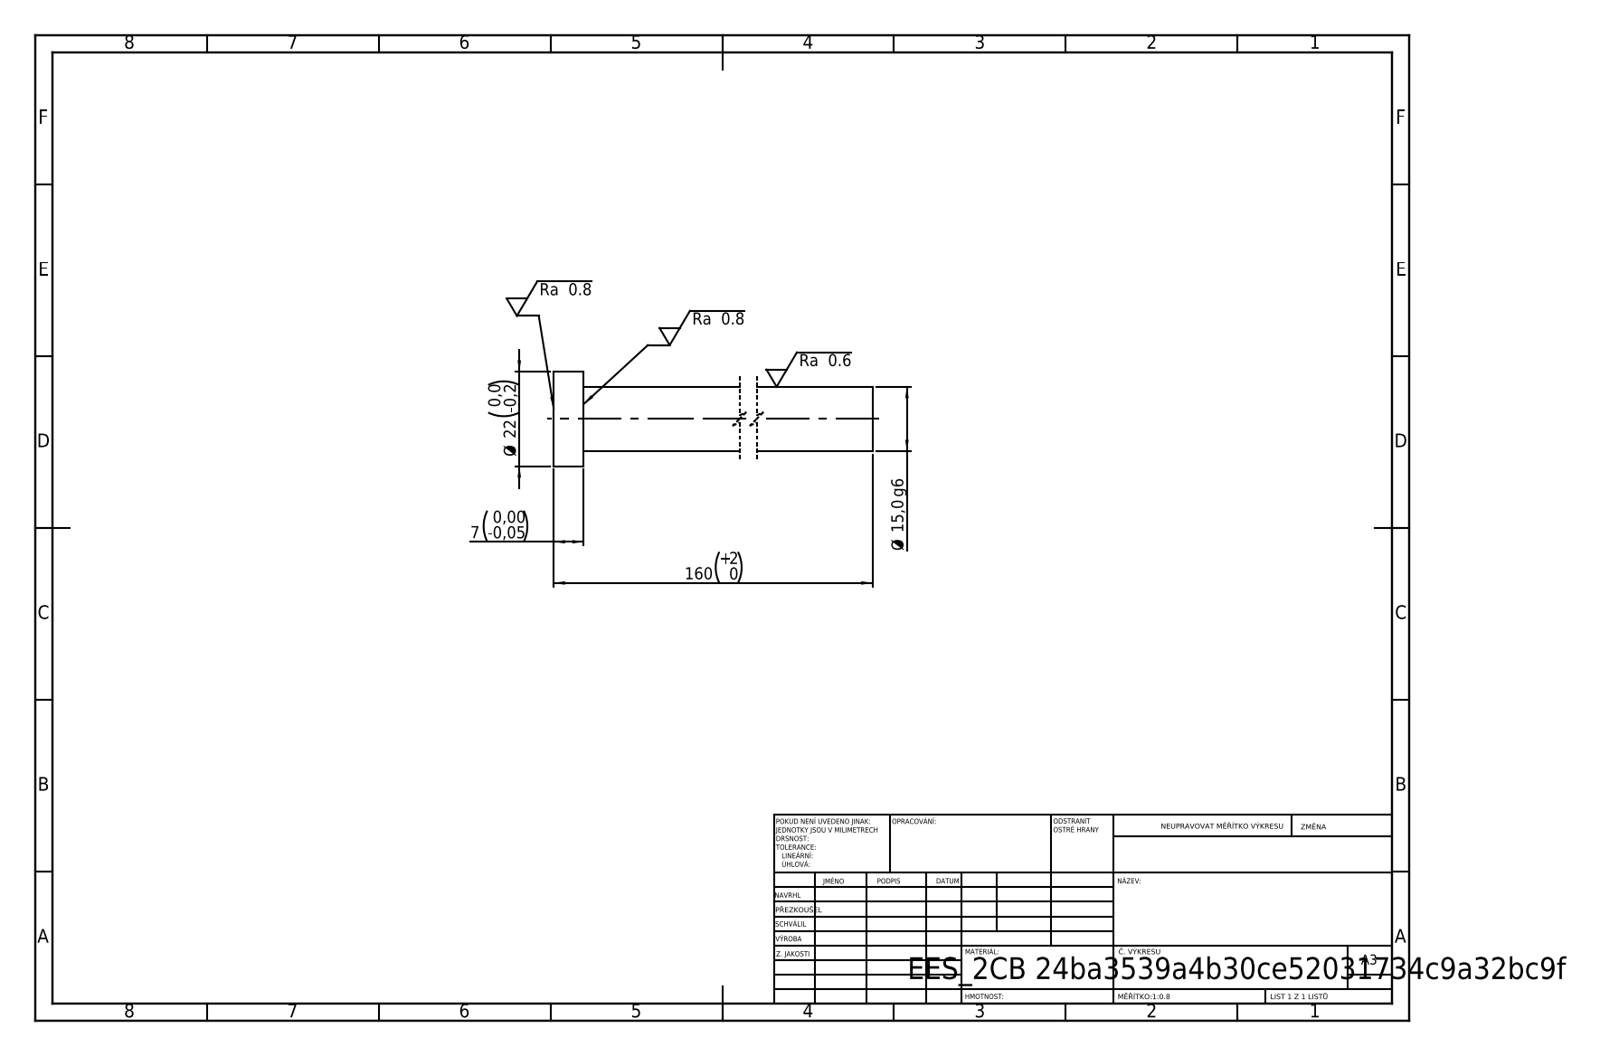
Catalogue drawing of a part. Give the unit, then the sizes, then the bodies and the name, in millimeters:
Units: millimetres
Overall size (bounding box): 160 × 22 × 22
Round bosses / shafts (diameter × count): ⌀22 ×1, ⌀15 ×1
Main face-to-face distances: 7, 160, 153
Volume: 29 698 mm³ · Surface area: 8 454 mm²
Bodies: 1 solid, 7 faces (3 planar, 4 cylindrical, 0 other)
STEP written by: SolidWorks 2019 (CONFIG_CONTROL_DESIGN)
